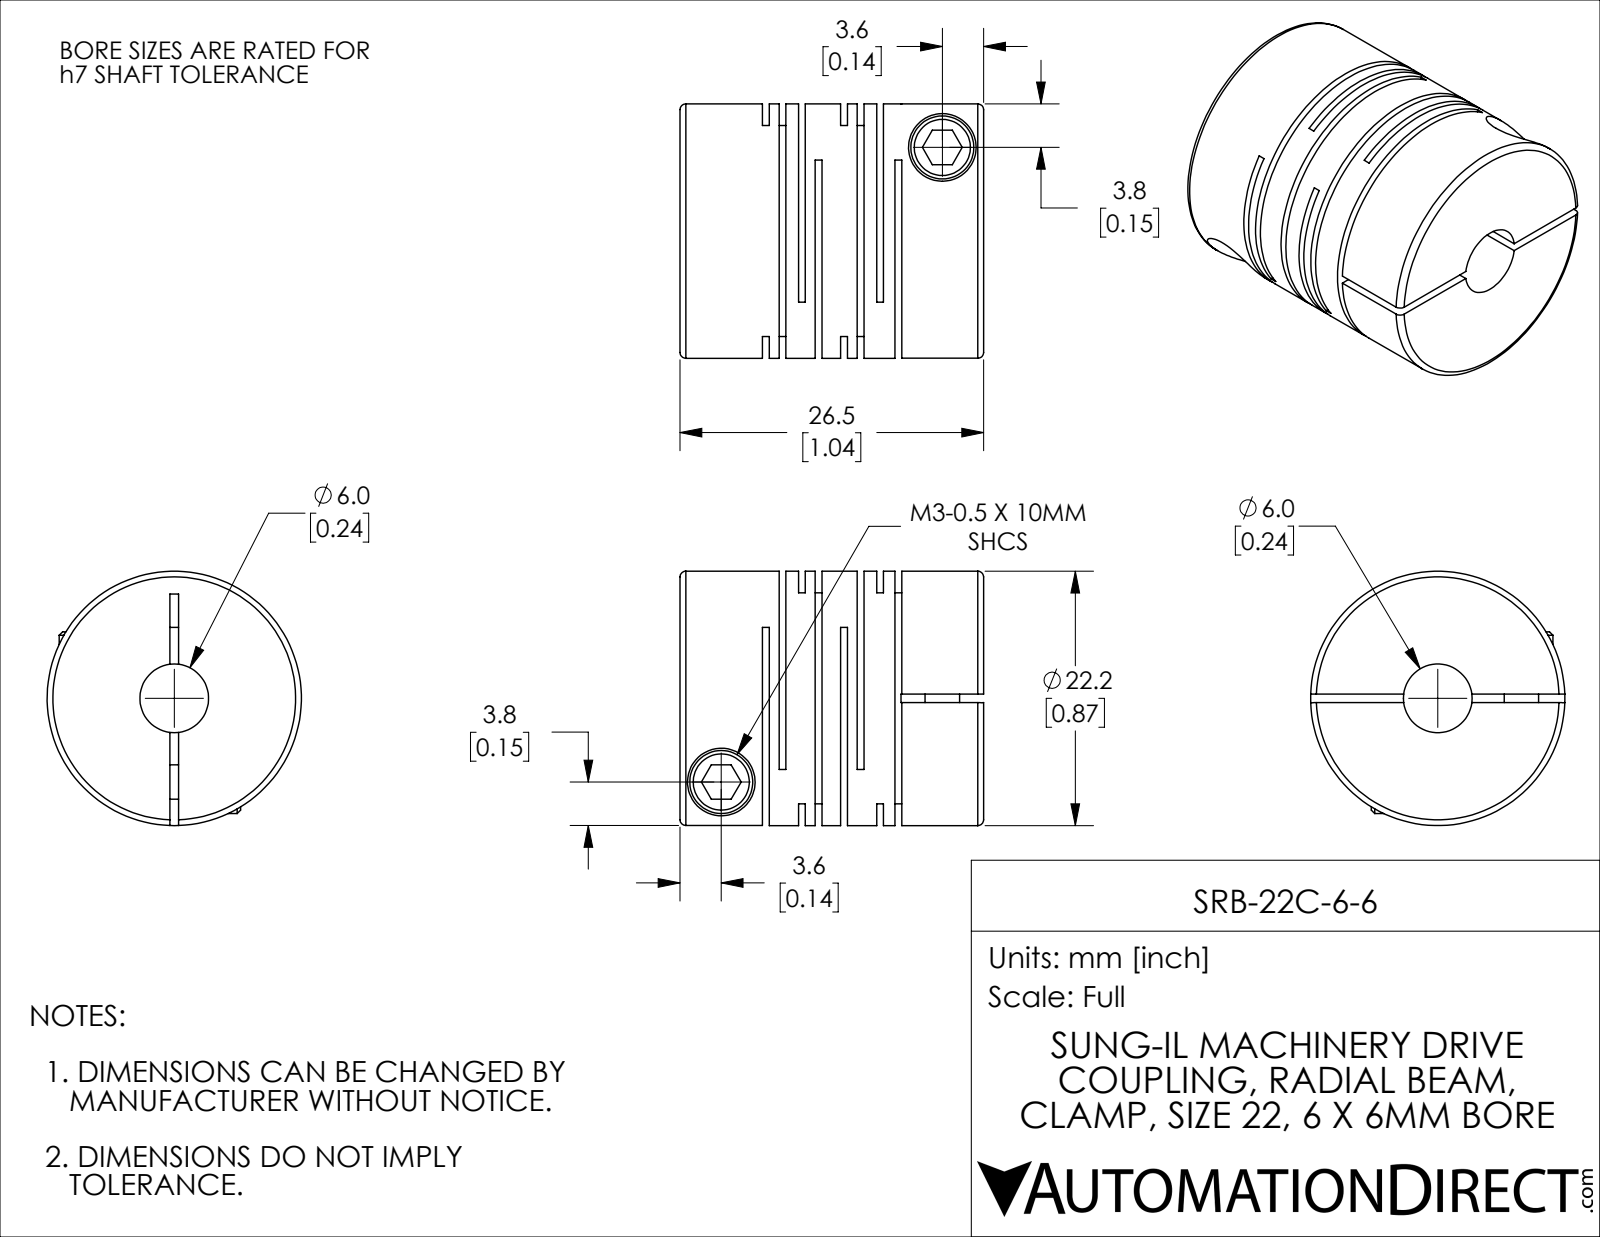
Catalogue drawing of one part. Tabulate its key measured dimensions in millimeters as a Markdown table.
| quantity | value |
| --- | --- |
| part name | SRB-22C-6-6 |
| STEP written by | SolidWorks 2021 (CONFIG_CONTROL_DESIGN) |
| units | millimeters |
| bodies | 1 solid, 115 faces (60 planar, 42 cylindrical, 13 other) |
| overall size | 26.5 × 22.2 × 22.2 |
| volume | 7 768 mm³ |
| surface area | 8 170 mm² |
| round holes (diameter × count) | 3 × 2, 5.9 × 2, 6 × 1 |
| round bosses / shafts (diameter × count) | 5.5 × 2, 22.2 × 1 |
| main face-to-face distances | 0.59, 6.82, 3.15, 1.45, 5.37, 1.7, 3.67, 6.23, 0.86, 2.56 |
